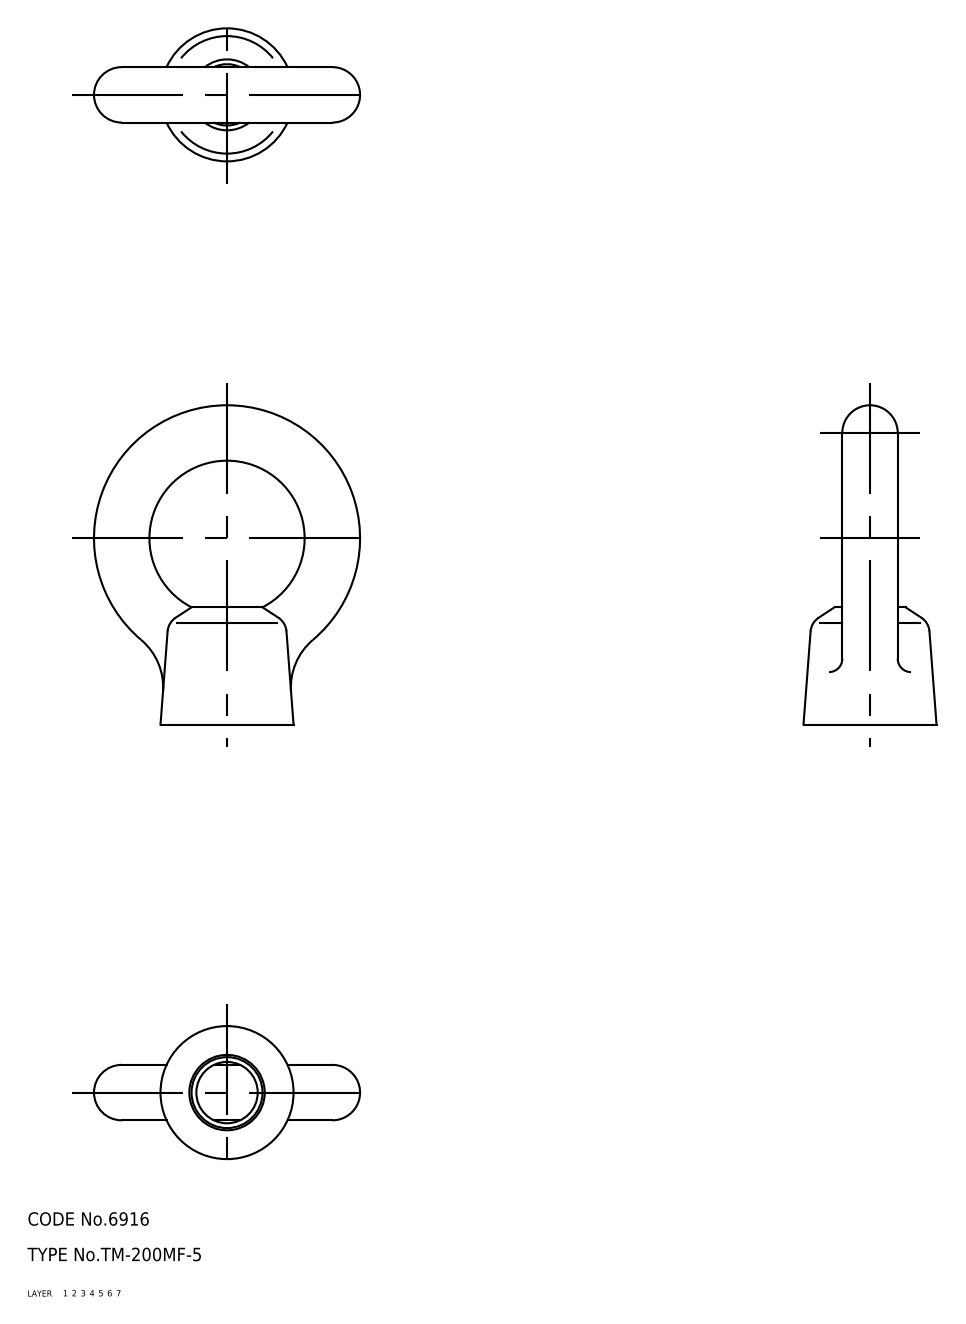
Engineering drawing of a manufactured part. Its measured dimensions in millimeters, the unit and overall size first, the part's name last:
Units: millimetres
Overall size (bounding box): 72 × 60 × 30
Round holes (diameter × count): ⌀16 ×1
Volume: 25 997 mm³ · Surface area: 8 922 mm²
Bodies: 1 solid, 19 faces (1 planar, 2 cylindrical, 16 other)
Part name (STEP PRODUCT): TM_200MF_5
STEP written by: SolidWorks 2003240 (AUTOMOTIVE_DESIGN)
